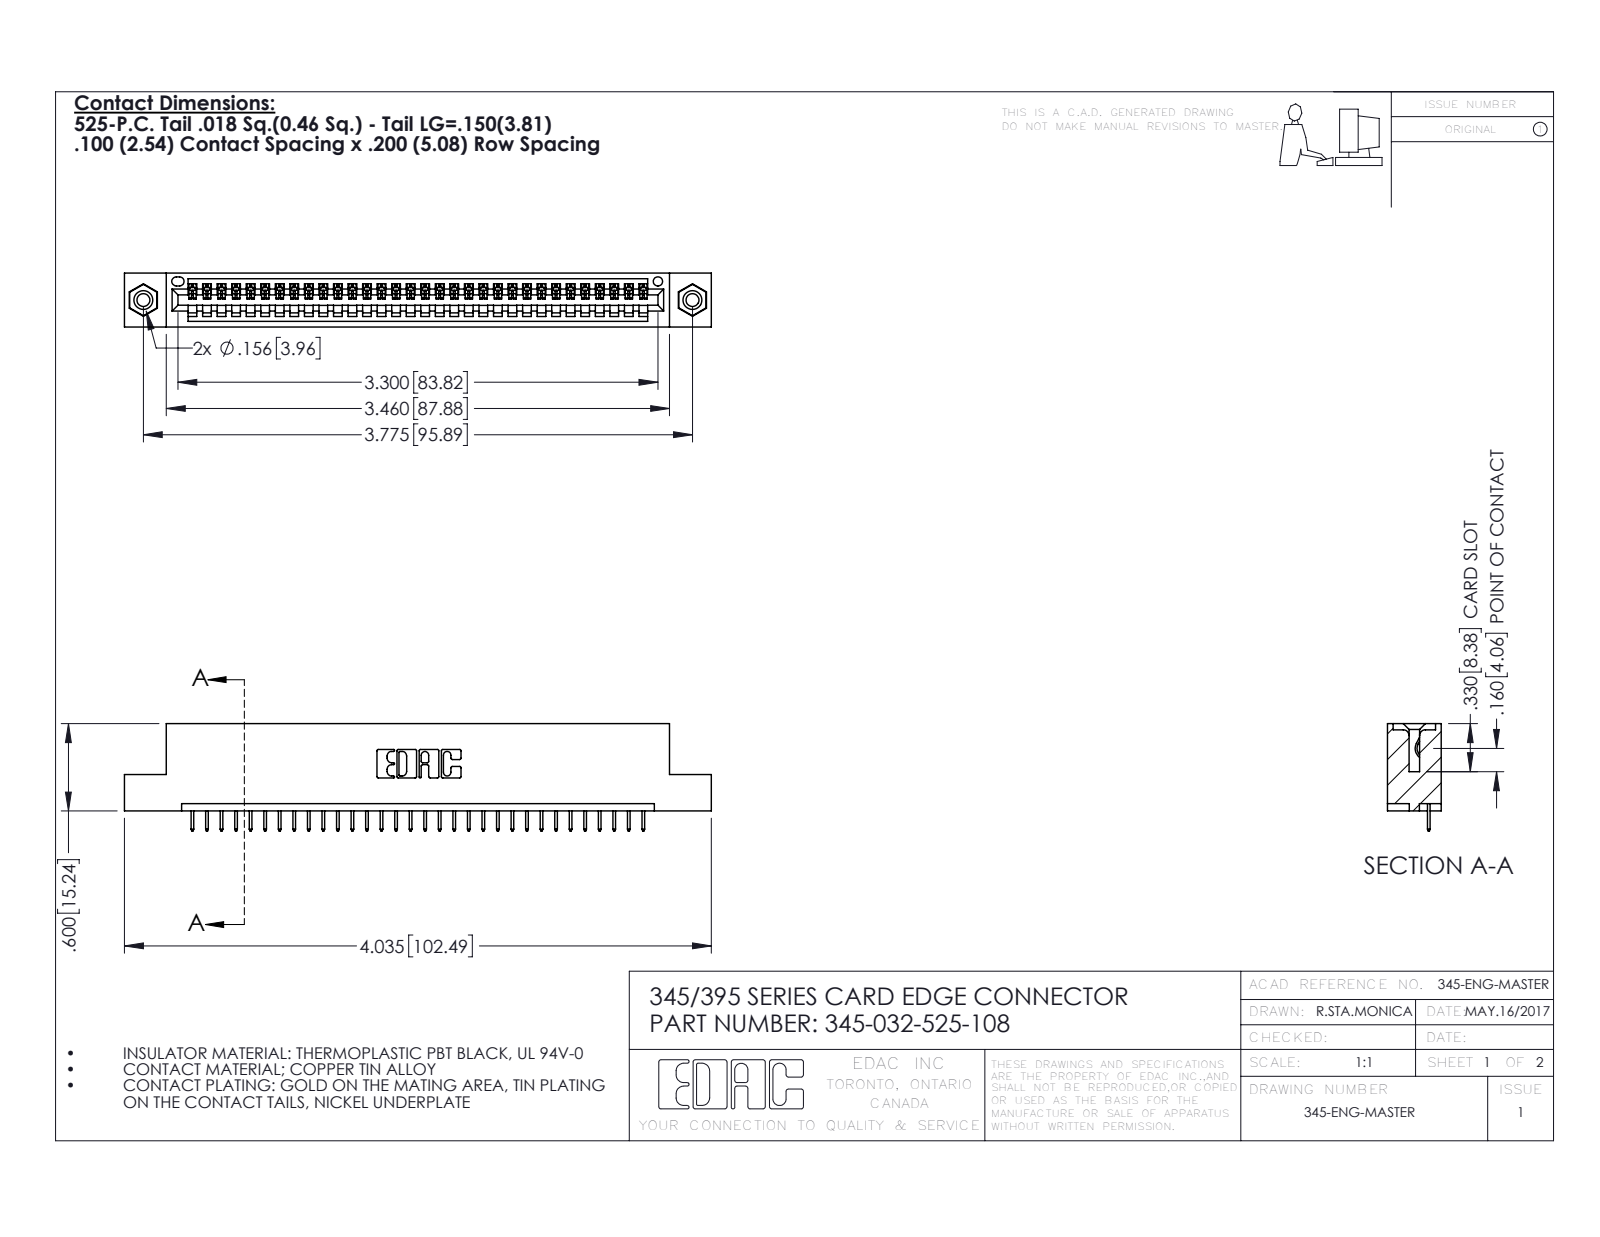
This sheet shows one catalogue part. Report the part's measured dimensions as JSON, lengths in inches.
{"part_name": "345-250-001_345-250-003-102; 345-032-525-108; 345-292-001_345-293-125; 345 Part_Flush Mounting Lugs - 0.156 Dia-TI", "step_written_by": "SolidWorks 2020 (CONFIG_CONTROL_DESIGN)", "units": "inches", "bodies": {"solids": 35, "faces": 2170, "planar": 1584, "cylindrical": 570, "other": 16}, "overall_size": [4.035, 0.737, 0.37], "volume_in3": 0.581, "surface_area_in2": 18.74, "round_holes": [[0.089, 2], [0.125, 2], [0.156, 2], [0.064, 1]], "round_bosses_or_shafts": [[0.155, 2]], "partial_cylinders_radius": [[0.006, 64], [0.01, 22], [0.007, 6], [0.031, 6], [0.026, 3], [0.031, 2], [0.04, 2], [0.014, 1]], "face_to_face_distances": [0.072, 0.298, 0.37, 0.2, 0.098, 0.272, 0.025, 0.225, 0.072, 0.149], "hole_center_spacings": [0.27, 3.54, 3.775]}
